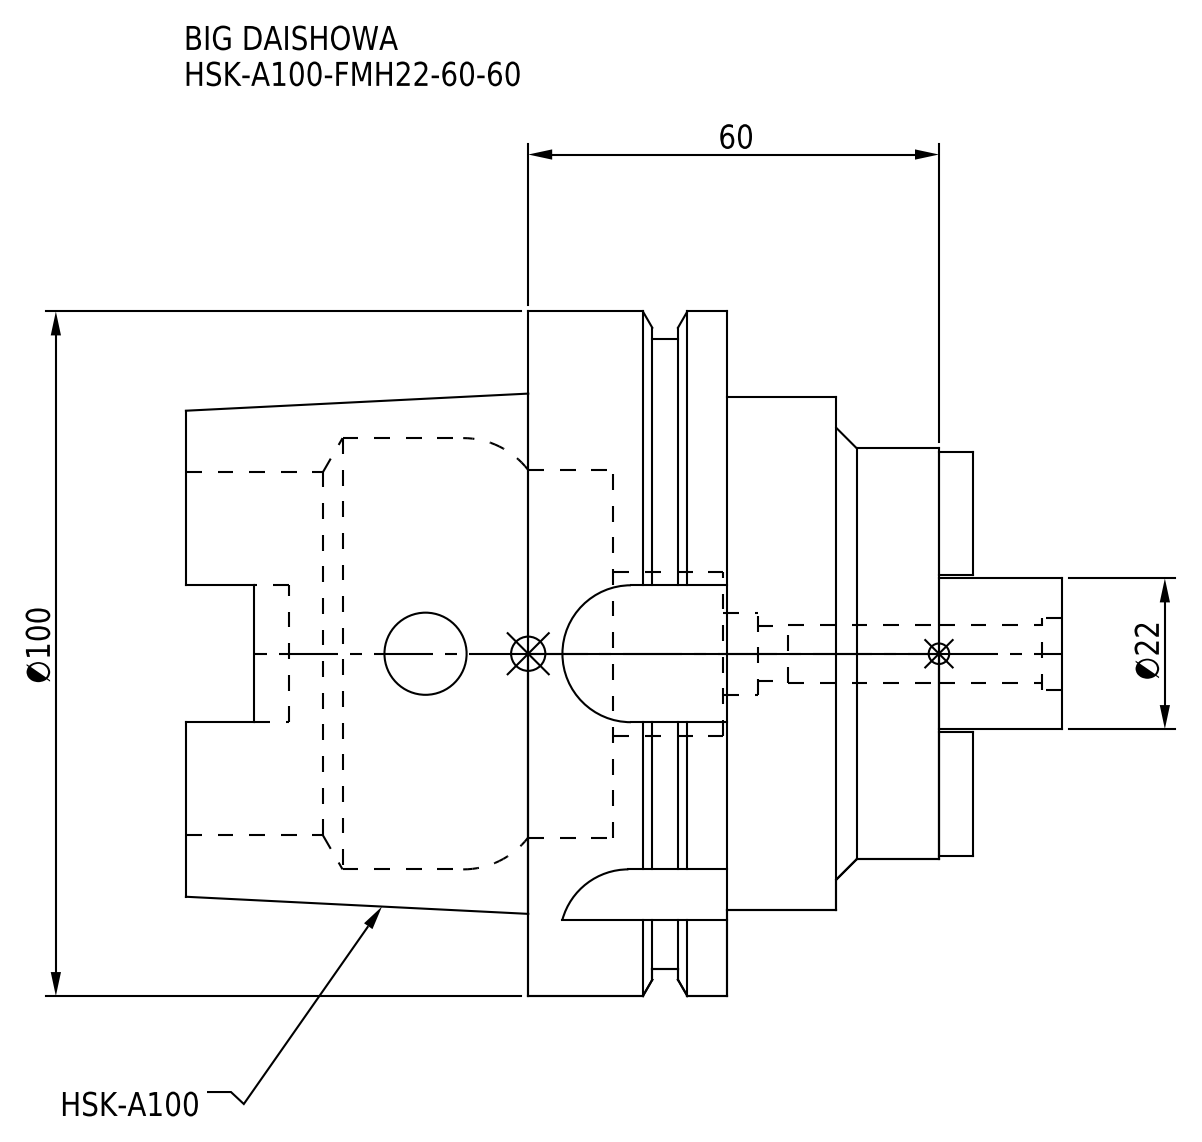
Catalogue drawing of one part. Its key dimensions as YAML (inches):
part_name: "HSK-A100-FMH22-60-60"
step_written_by: "CREO PARAMETRIC BY PTC INC, 2016380 (AUTOMOTIVE_DESIGN)"
units: inches
bodies: {solids: 1, faces: 109, planar: 47, cylindrical: 46, other: 16}
overall_size: [5.039, 3.937, 3.937]
volume: 22.76
surface_area: 92.02
round_holes:
  - {diameter: 0.472, count: 2}
  - {diameter: 0.315, count: 1}
  - {diameter: 0.335, count: 1}
  - {diameter: 0.413, count: 1}
  - {diameter: 0.945, count: 1}
  - {diameter: 2.087, count: 1}
  - {diameter: 2.118, count: 1}
  - {diameter: 2.48, count: 1}
round_bosses_or_shafts:
  - {diameter: 3.937, count: 1}
  - {diameter: 3.622, count: 1}
  - {diameter: 2.953, count: 1}
  - {diameter: 2.362, count: 1}
  - {diameter: 0.866, count: 1}
partial_cylinders:
  - {radius: 0.192, count: 4}
  - {radius: 0.394, count: 4}
face_to_face_distances: [1.142, 0.652, 2.362, 1.22, 1.872, 0.49, 0.63, 0.591, 3.74, 4.331]
